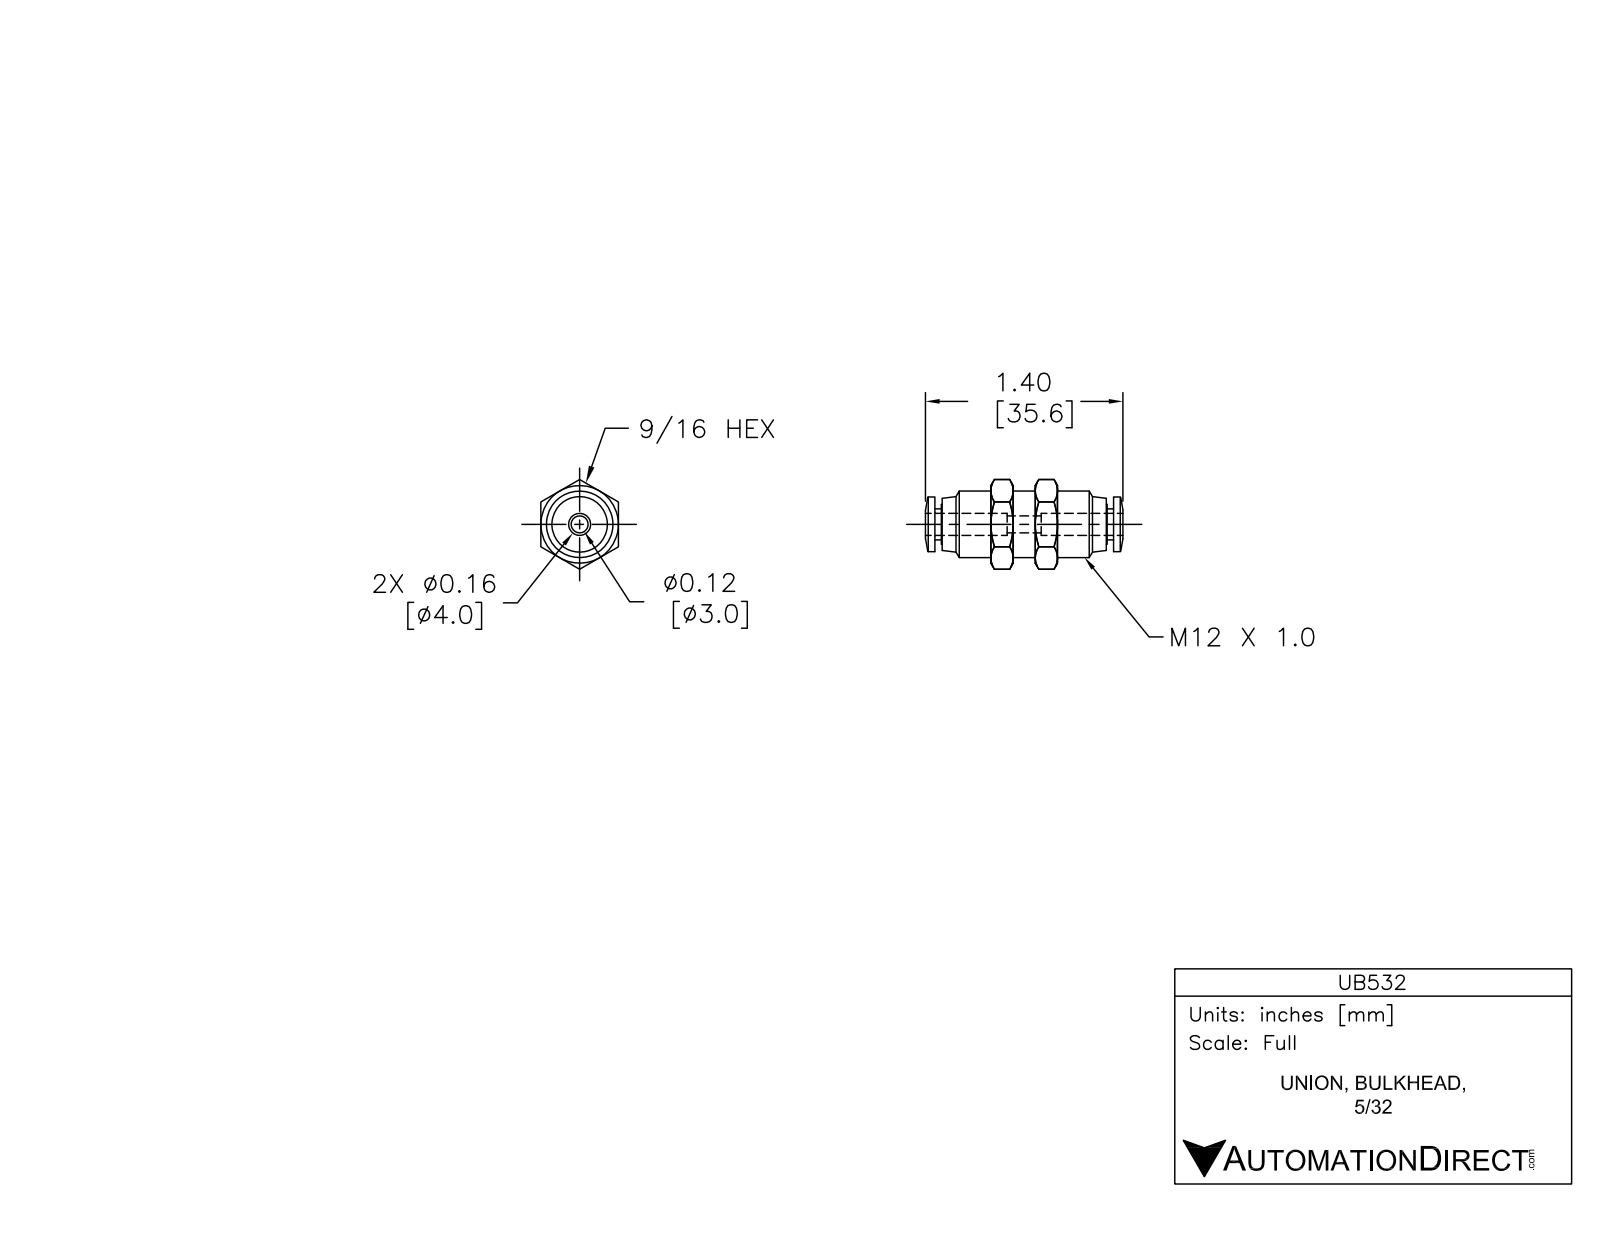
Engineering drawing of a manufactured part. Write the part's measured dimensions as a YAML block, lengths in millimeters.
part_name: "UB532"
step_written_by: "SolidWorks 2015 (AUTOMOTIVE_DESIGN)"
units: millimeters
bodies: {solids: 1, faces: 96, planar: 24, cylindrical: 24, other: 48}
overall_size: [35.6, 16.2, 14]
volume: 3410
surface_area: 2307
round_holes:
  - {diameter: 3, count: 1}
  - {diameter: 4.3, count: 1}
round_bosses_or_shafts:
  - {diameter: 12, count: 1}
  - {diameter: 9.9, count: 1}
  - {diameter: 7.2, count: 1}
  - {diameter: 5.6, count: 1}
face_to_face_distances: [14, 4, 14.1, 18.1, 10.1, 22.1, 8, 1.3, 30.9, 8.8]
